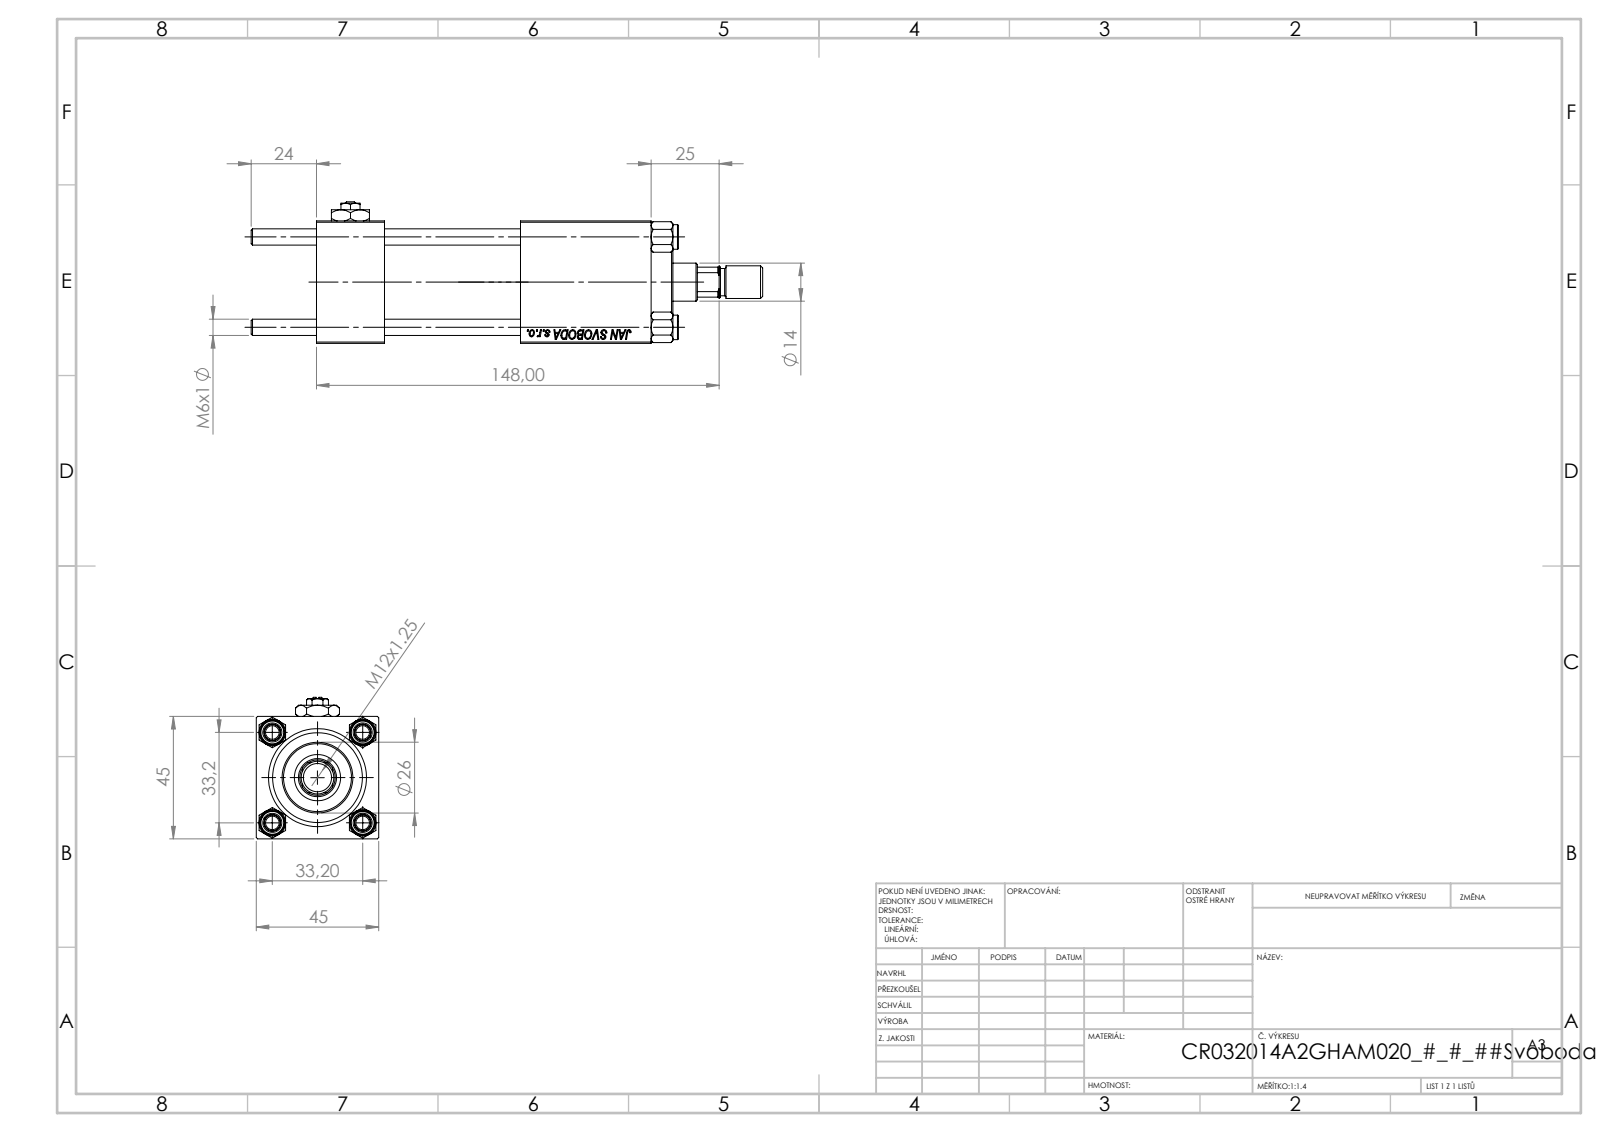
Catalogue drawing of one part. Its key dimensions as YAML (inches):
part_name: "NUT_M5; CR025_012_A_0_G_A_G_M_020_+#_##_TYCINKA; Zatka_pro_OIL_PORT; V215CR_BODY_A (+3 more)"
step_written_by: "SolidWorks 2019 (CONFIG_CONTROL_DESIGN)"
units: inches
bodies: {solids: 13, faces: 1198, planar: 546, cylindrical: 88, other: 564}
overall_size: [7.402, 2.047, 1.772]
volume: 12.16
surface_area: 115.9
round_holes:
  - {diameter: 0.236, count: 4}
  - {diameter: 0.276, count: 2}
  - {diameter: 0.518, count: 2}
  - {diameter: 0.787, count: 2}
  - {diameter: 0.256, count: 1}
  - {diameter: 0.551, count: 1}
  - {diameter: 0.669, count: 1}
  - {diameter: 0.945, count: 1}
  - {diameter: 1.26, count: 1}
  - {diameter: 1.299, count: 1}
round_bosses_or_shafts:
  - {diameter: 0.354, count: 4}
  - {diameter: 1.496, count: 1}
  - {diameter: 1.024, count: 1}
  - {diameter: 0.472, count: 1}
  - {diameter: 0.394, count: 1}
partial_cylinders:
  - {radius: 0.256, count: 1}
face_to_face_distances: [1.772, 0.984, 4.843, 3.858, 1.969, 2.953, 1.89, 3.713, 2.728, 0.76]
hole_center_spacings: [0.924, 1.307, 1.848, 2.972]
